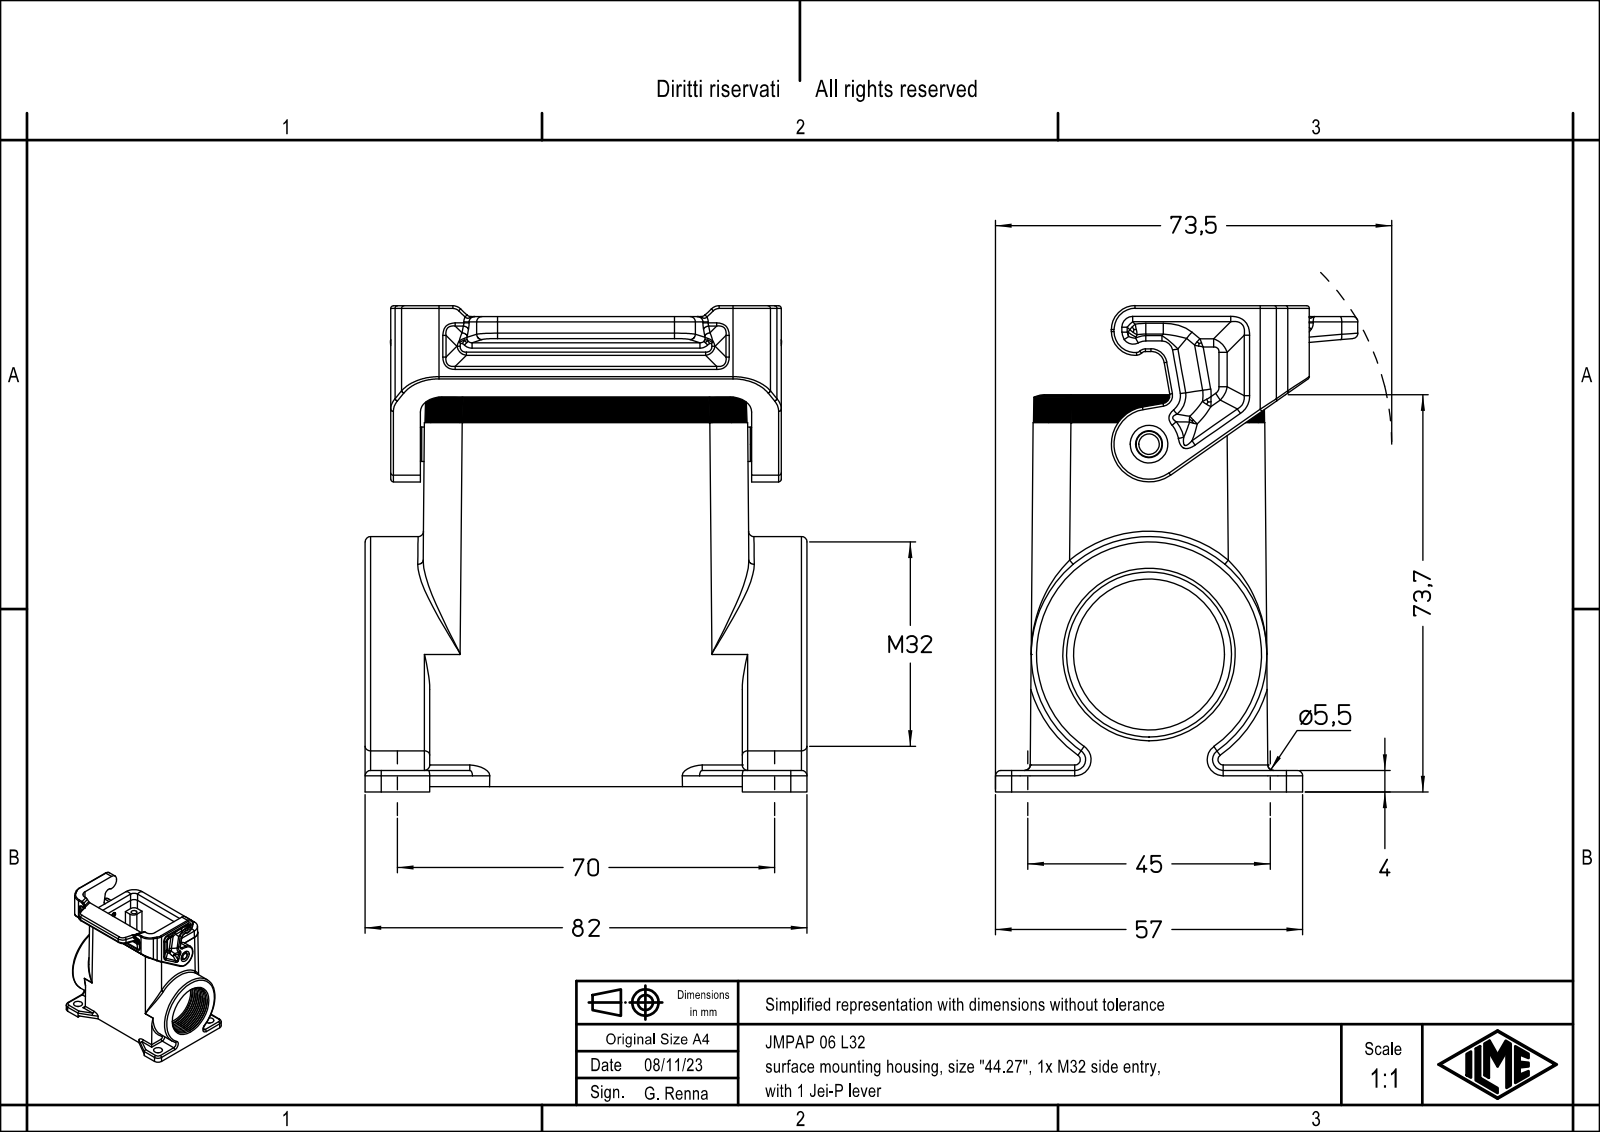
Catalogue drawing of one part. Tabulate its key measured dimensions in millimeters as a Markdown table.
| quantity | value |
| --- | --- |
| part name | JMPAP 06 L32 |
| STEP written by | Creo Elements/Direct Modeling 20.1B 02-Apr-2019 (C) Parametric Technology GmbH (AUTOMOTIVE_DESIGN) |
| units | millimeters |
| bodies | 1 solid, 515 faces (121 planar, 176 cylindrical, 218 other) |
| overall size | 90.2 × 82 × 67.25 |
| volume | 109 921 mm³ |
| surface area | 45 710 mm² |
| round holes (diameter × count) | 3.5 × 4, 28 × 1, 30.6 × 1 |
| round bosses / shafts (diameter × count) | 43.75 × 1, 6.4 × 1, 4.8 × 1 |
| partial cylindrical surfaces (radius × count) | 1 × 31, 3 × 28, 0.5 × 18, 2 × 18, 7 × 9, 4 × 8, 6 × 6, 1.5 × 2 |
| main face-to-face distances | 10.25, 3, 71.75, 1, 4, 61.5, 7, 82, 20.5, 51.25 |
| hole center spacings | 27, 44, 51.62 |
